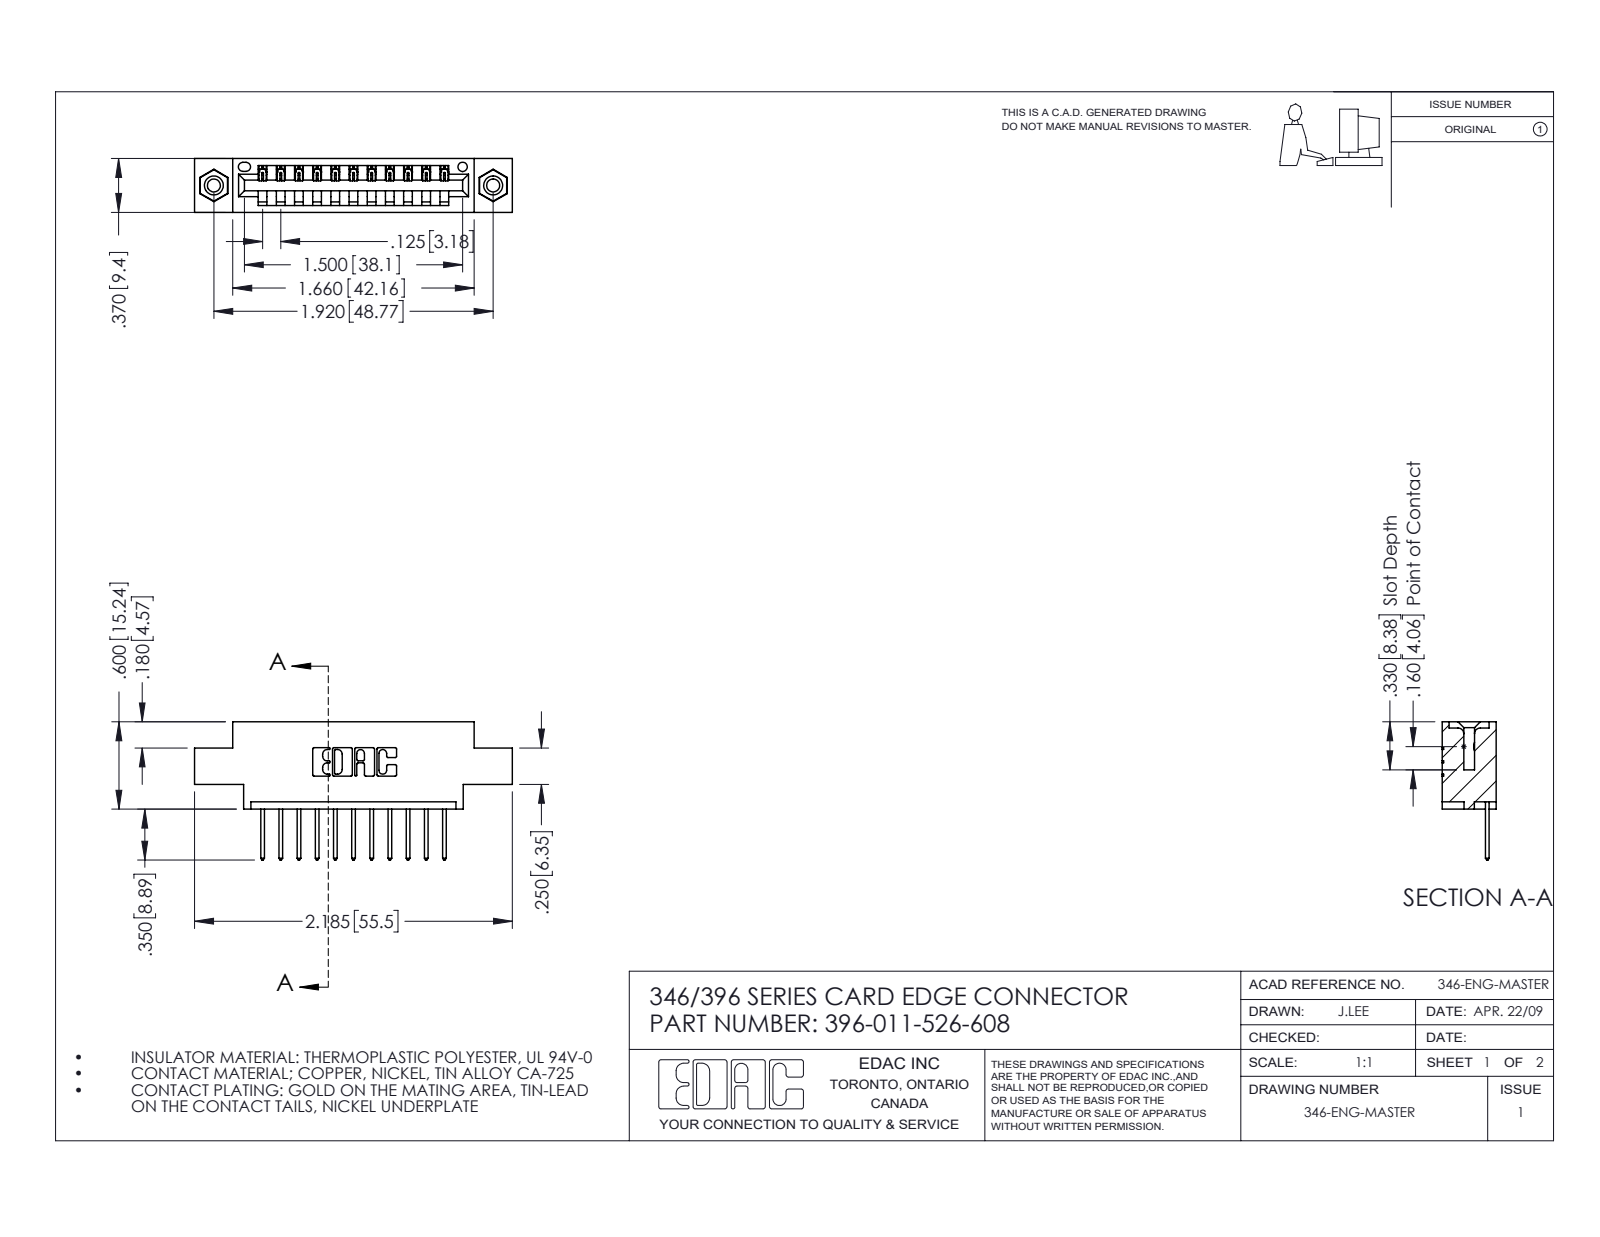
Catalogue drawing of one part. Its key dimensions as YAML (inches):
part_name: "396-011-526-608; 346 Part_0.170 Offset - 0.156 Dia-TI; 345-250-001_345-250-003-102; 345-292-001_345-293-126"
step_written_by: "SolidWorks 2016 (CONFIG_CONTROL_DESIGN)"
units: inches
bodies: {solids: 14, faces: 824, planar: 552, cylindrical: 256, other: 16}
overall_size: [2.185, 0.95, 0.37]
volume: 0.301
surface_area: 9.296
round_holes:
  - {diameter: 0.089, count: 2}
  - {diameter: 0.125, count: 2}
  - {diameter: 0.156, count: 2}
  - {diameter: 0.064, count: 1}
round_bosses_or_shafts:
  - {diameter: 0.155, count: 2}
partial_cylinders:
  - {radius: 0.006, count: 22}
  - {radius: 0.01, count: 22}
  - {radius: 0.01, count: 22}
  - {radius: 0.007, count: 6}
  - {radius: 0.031, count: 6}
  - {radius: 0.026, count: 3}
  - {radius: 0.031, count: 2}
  - {radius: 0.04, count: 2}
face_to_face_distances: [0.25, 0.37, 0.048, 0.322, 0.222, 0.072, 0.298, 0.025, 0.148, 0.1]
hole_center_spacings: [0.246, 1.715, 1.92]
